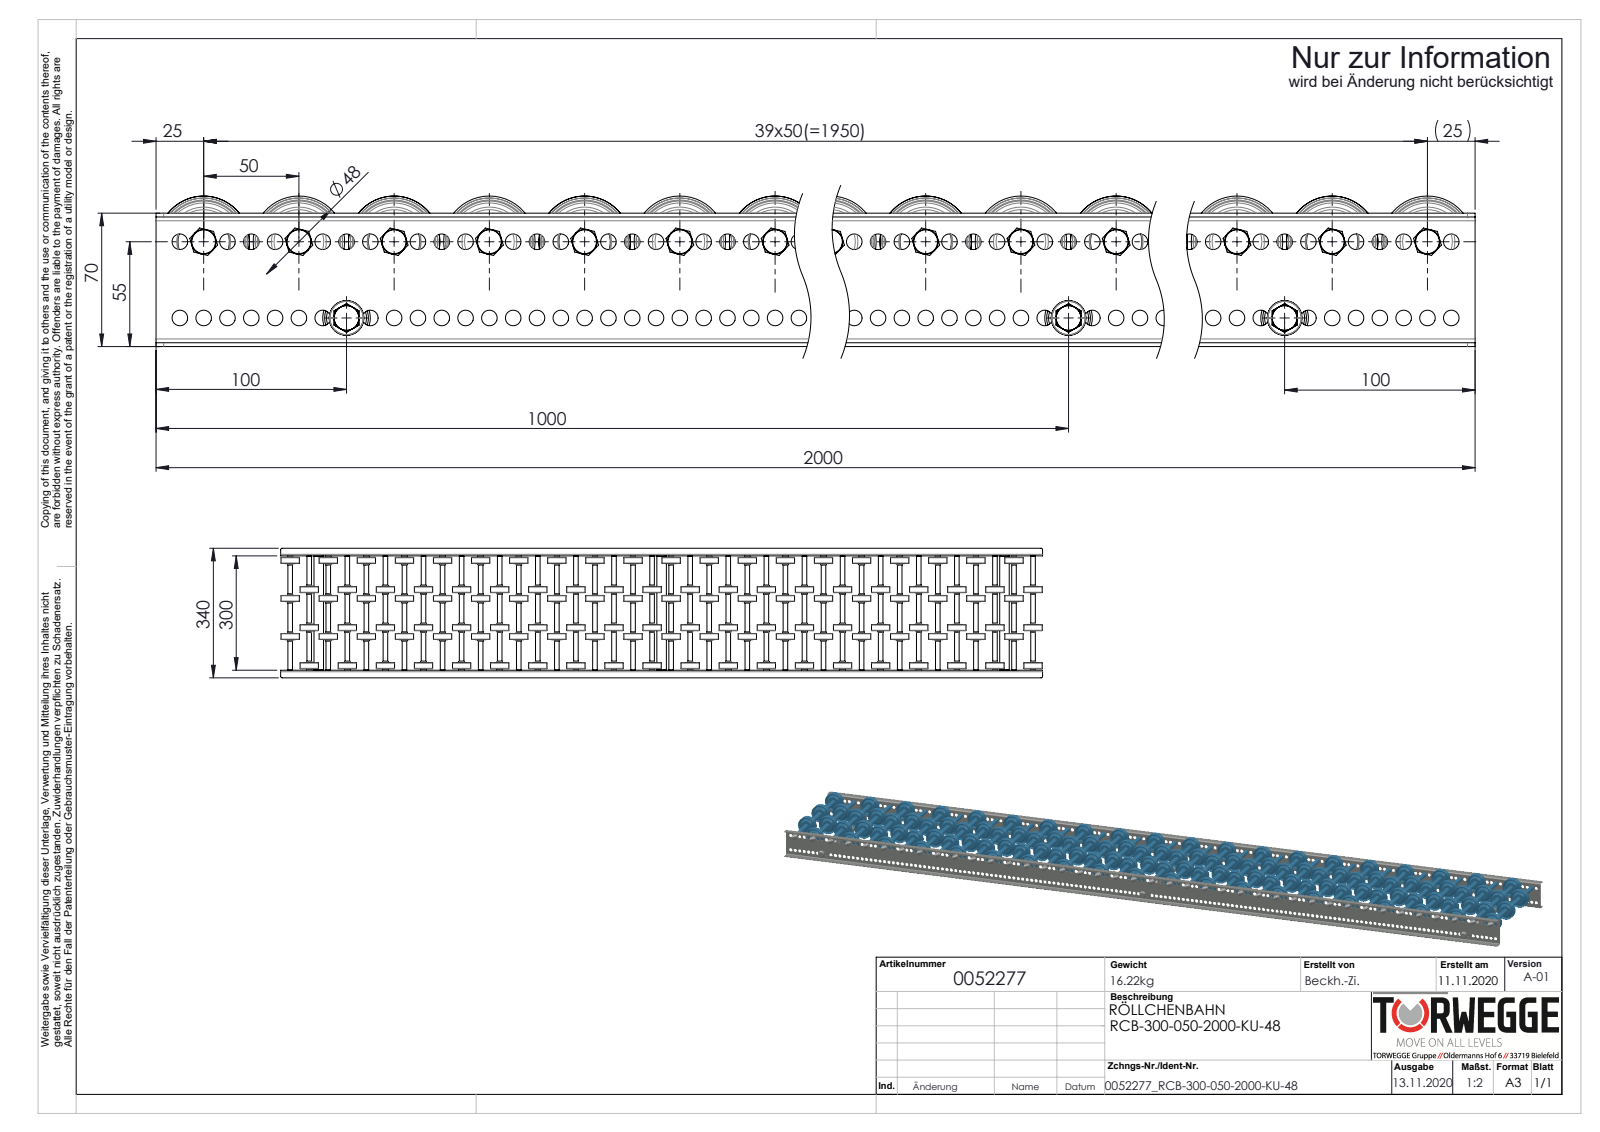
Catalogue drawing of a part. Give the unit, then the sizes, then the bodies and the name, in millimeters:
Units: millimetres
Overall size (bounding box): 2000 × 340 × 79
Round holes (diameter × count): ⌀8.2 ×318, ⌀6.65 ×40, ⌀9.65 ×40, ⌀13.7 ×40, ⌀6.8 ×3, ⌀21 ×3
Round bosses / shafts (diameter × count): ⌀8 ×43, ⌀48 ×40, ⌀27 ×40, ⌀12.7 ×40, ⌀12.5 ×40, ⌀12 ×40, ⌀25 ×3
Partial cylindrical surfaces — rounded edges, fillets, slot ends (radius × count): R4 ×8, R2 ×4
Main face-to-face distances: 2, 302, 68, 304, 300, 99.8, 70, 66, 16.3, 76.1
Hole centre spacings: 12.5, 25, 37.5, 50, 62.5, 75, 87.5, 100
Volume: 4 313 000 mm³ · Surface area: 3 140 000 mm²
Bodies: 377 solids, 13226 faces (2442 planar, 4388 cylindrical, 6396 other)
Part name (STEP PRODUCT): 0052277; Röllchenachse-für-Konfiguration_EL300; 0011532_2300-48-8; Hutmutter_DIN_1587_M8 (+5 more)
STEP written by: SolidWorks 2020 (AUTOMOTIVE_DESIGN)
